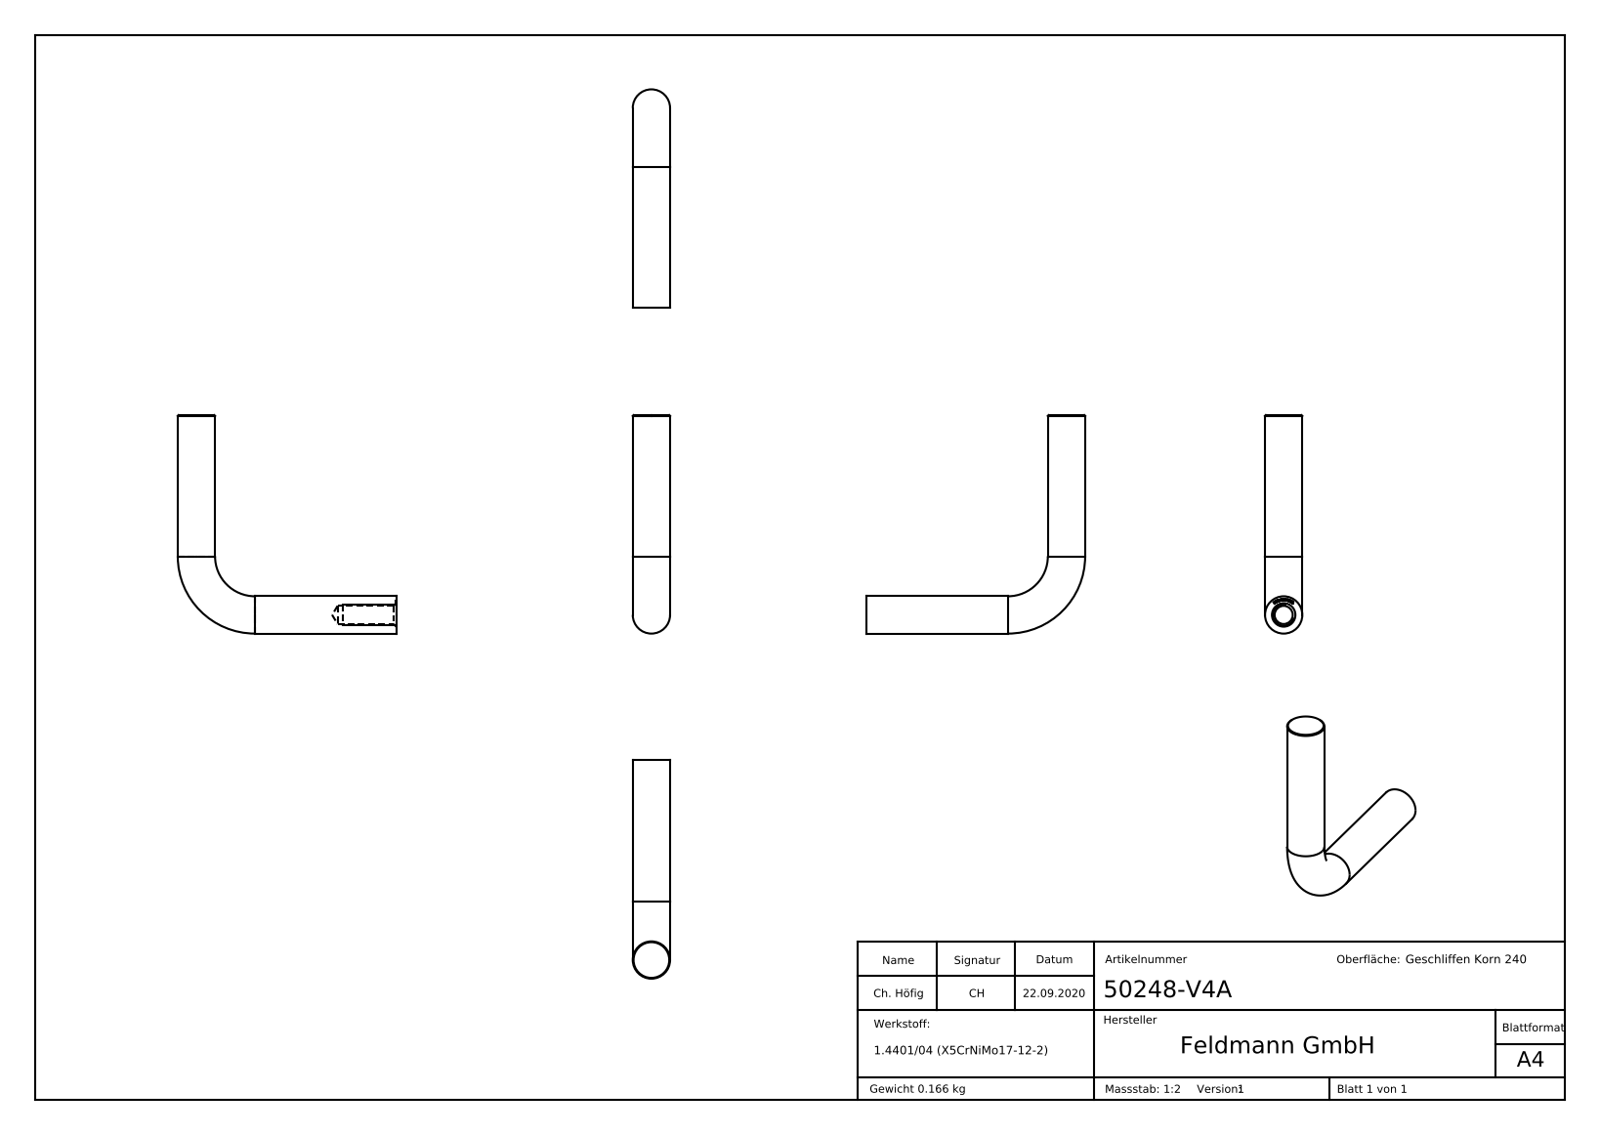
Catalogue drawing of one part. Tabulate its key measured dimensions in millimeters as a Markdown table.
| quantity | value |
| --- | --- |
| part name | 50248-V4A |
| STEP written by | SolidWorks 2018 (CONFIG_CONTROL_DESIGN) |
| units | millimeters |
| bodies | 1 solid, 244 faces (142 planar, 6 cylindrical, 96 other) |
| overall size | 82 × 82 × 14 |
| volume | 20 800 mm³ |
| surface area | 6 951 mm² |
| round holes (diameter × count) | 6.8 × 1 |
| round bosses / shafts (diameter × count) | 14 × 2 |
| main face-to-face distances | 0.54, 0.58, 0.52, 0.34, 0.39, 0.32, 0.48, 0.31, 0.53, 0.37 |
